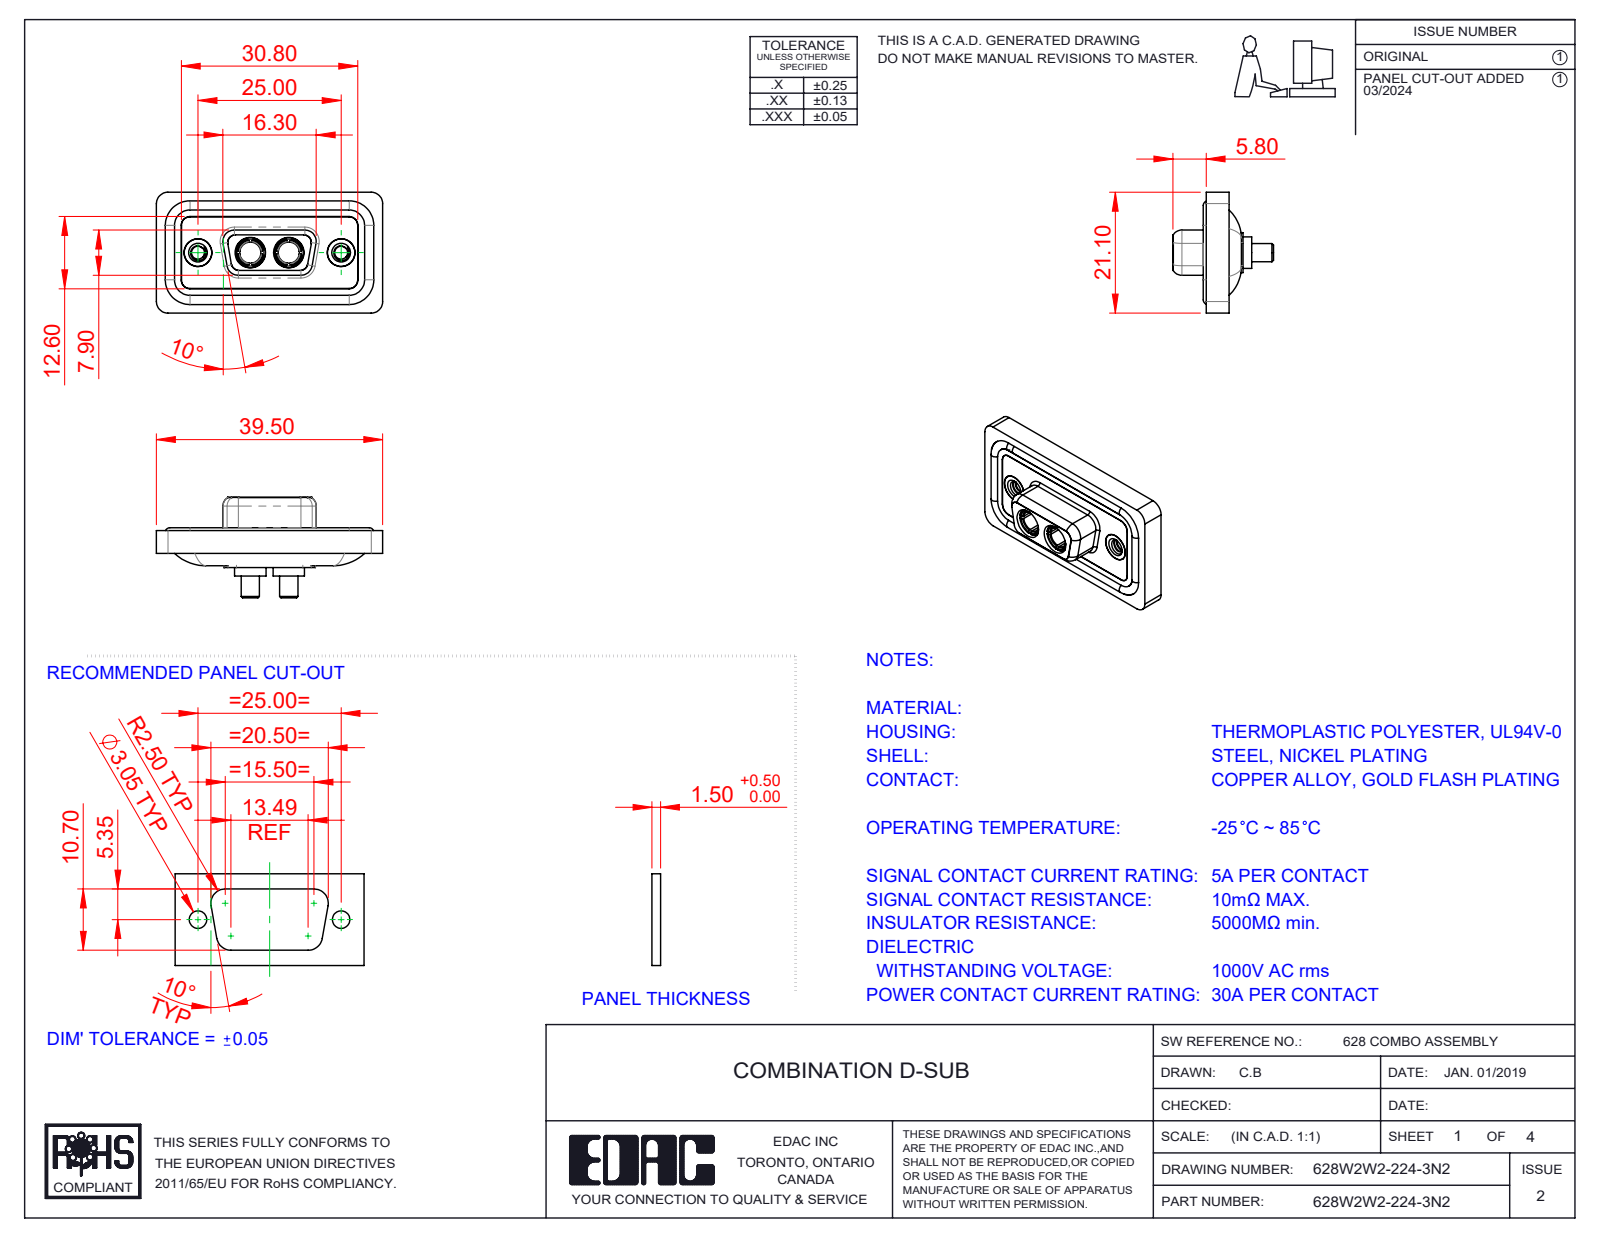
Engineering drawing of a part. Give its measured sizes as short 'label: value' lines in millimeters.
name: 628Combo Housing_2W2; 628Combo Waterproof Housing_09 Contacts; Power Socket_30A S; 628Combo Threaded Rivet_2 (+3 more)
written by: SolidWorks 2023 (CONFIG_CONTROL_DESIGN)
unit: mm
bodies: 11 solids, 534 faces (163 planar, 234 cylindrical, 137 other)
size: 39.5 × 21.1 × 17.55
volume: 4 727 mm³; area: 7 645 mm²
holes: 4× ⌀4.85, 2× ⌀2.26, 2× ⌀3.7, 2× ⌀4, 2× ⌀4.05, 2× ⌀5, 2× ⌀5.3
bosses: 4× ⌀1.6, 2× ⌀5.5, 2× ⌀5.2, 2× ⌀4.96, 2× ⌀4.95, 2× ⌀4.8, 2× ⌀4.75, 2× ⌀3.75
rounds: 22× R1.5, 18× R2, 8× R1.35, 8× R1.6, 4× R0.25, 4× R0.5, 4× R0.6, 4× R0.65
face distances: 0.4, 1.8, 1.1, 2.9, 0.5, 1.6, 5.65, 7.45, 1.5, 5.35
hole spacings: 9.14, 15.86, 6.72, 25
